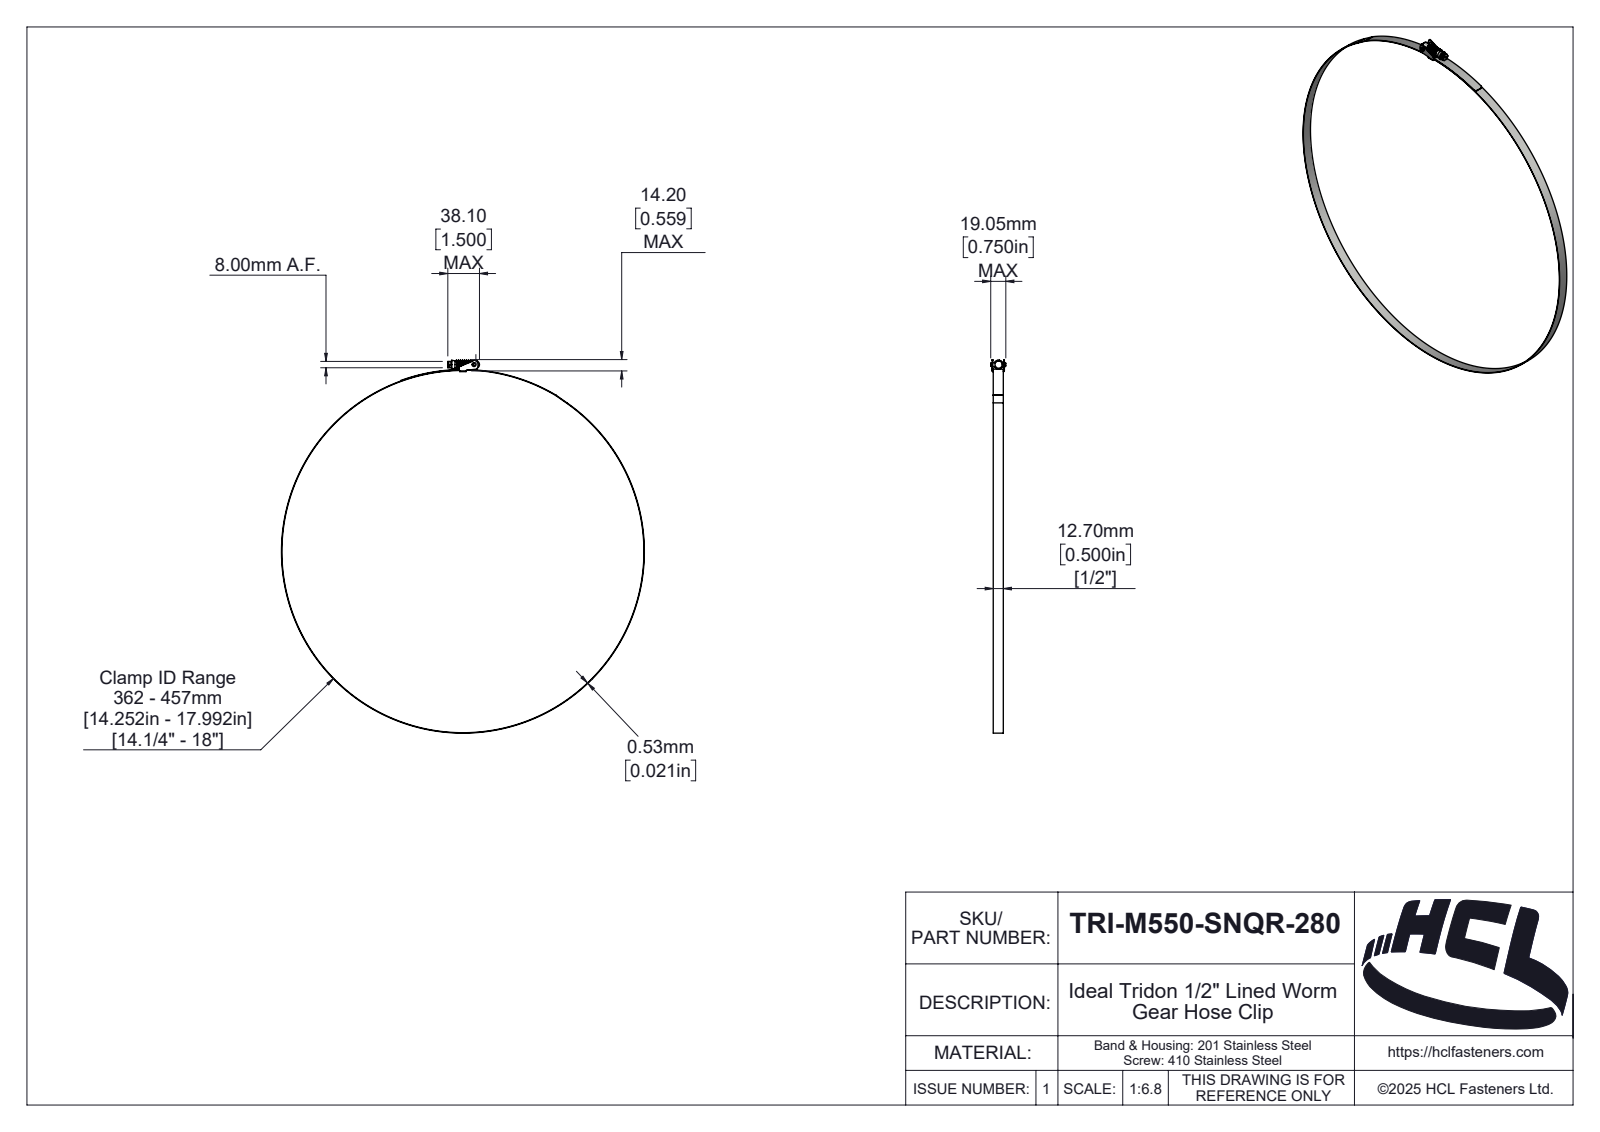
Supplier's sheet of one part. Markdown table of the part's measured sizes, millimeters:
| quantity | value |
| --- | --- |
| part name | TRI-M550-SNQR-280 |
| STEP written by | SolidWorks 2025 (AUTOMOTIVE_DESIGN) |
| units | millimeters |
| bodies | 5 solids, 222 faces (44 planar, 112 cylindrical, 66 other) |
| overall size | 471.02 × 458.06 × 19.05 |
| volume | 13 394 mm³ |
| surface area | 43 743 mm² |
| round holes (diameter × count) | 5 × 1, 457 × 1 |
| round bosses / shafts (diameter × count) | 458.06 × 1, 9.1 × 1 |
| partial cylindrical surfaces (radius × count) | 1 × 11, 0.1 × 2, 0.9 × 2, 3 × 2, 0.46 × 1, 1.89 × 1, 2 × 1, 2.35 × 1 |
| main face-to-face distances | 12.7, 0.8, 1.35, 14.05, 14.6, 0.55, 13.25, 0.53, 15.4, 13.8 |
| hole center spacings | 236.32 |
